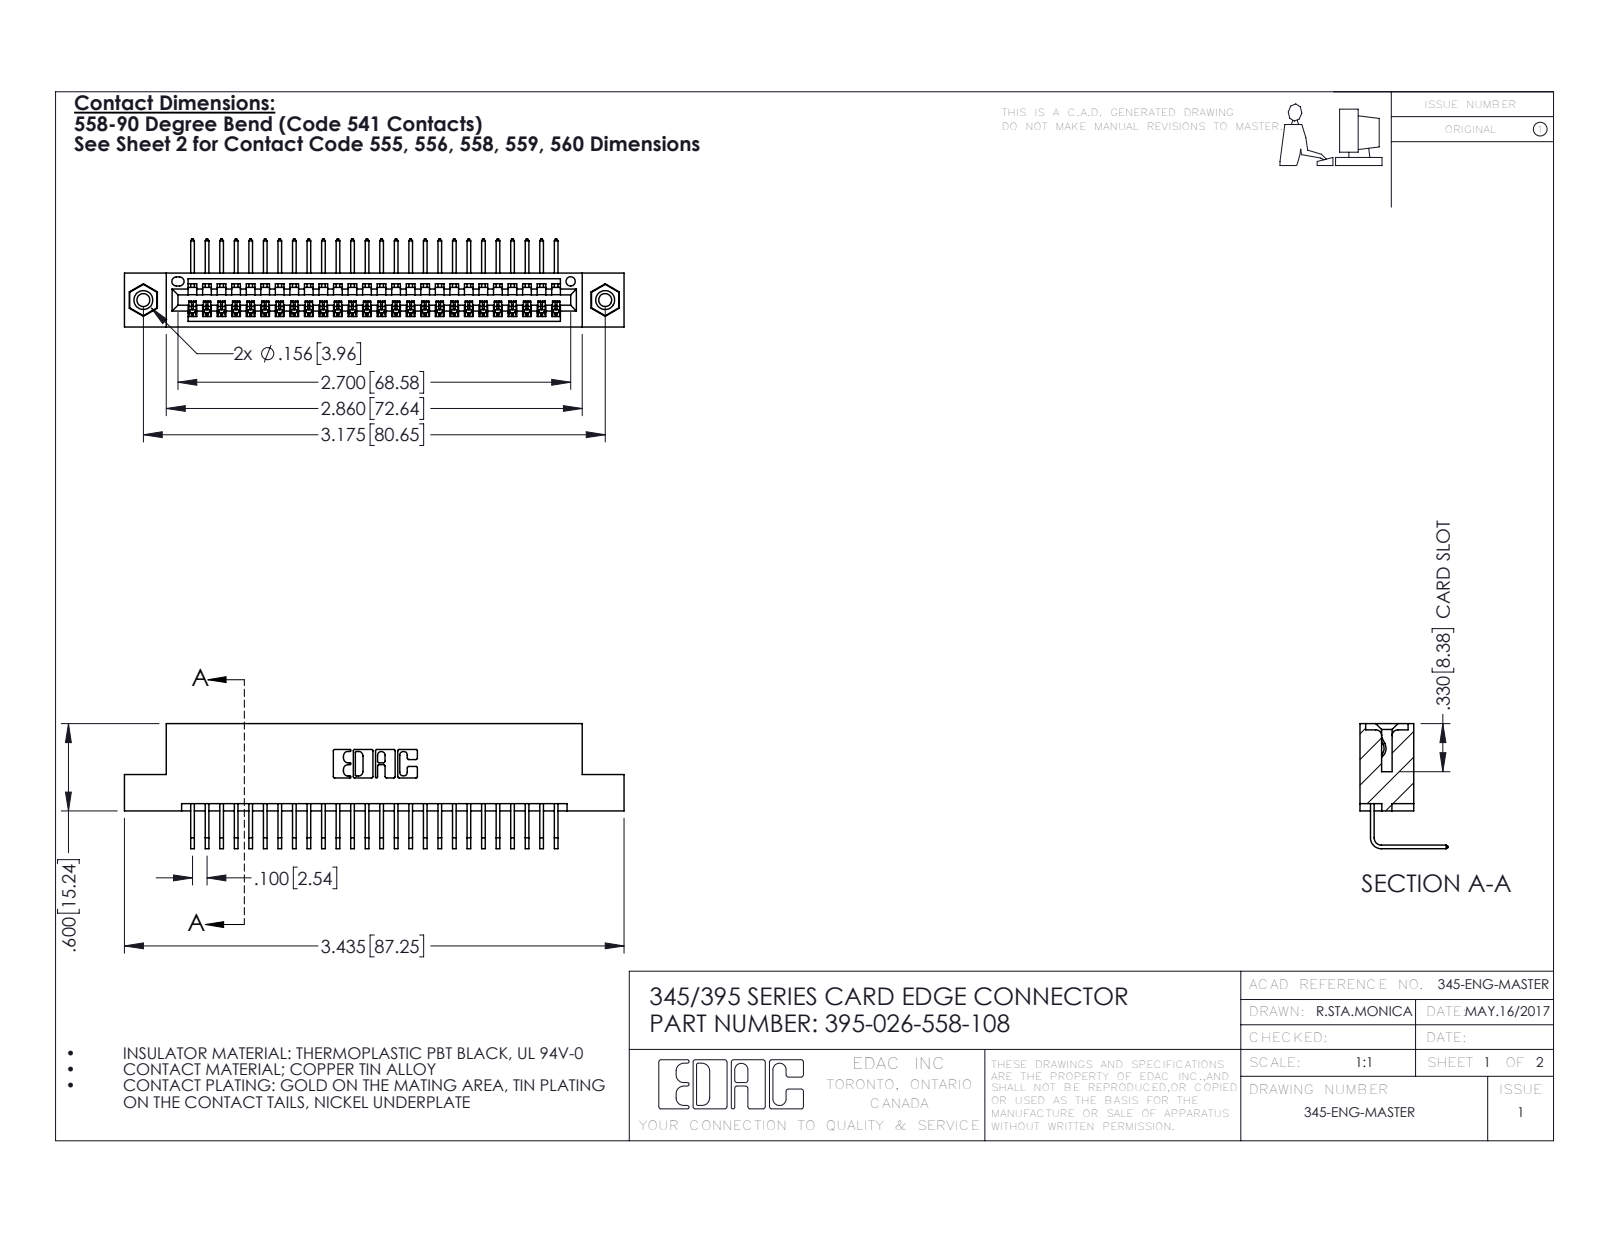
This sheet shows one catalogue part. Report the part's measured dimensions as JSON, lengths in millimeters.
{"part_name": "345-292-001_558 Tail - 2; 345-250-001_345-250-003-102; 345 Part_Flush Mounting Lugs - 0.156 Dia-TI; 395-026-558-108", "step_written_by": "SolidWorks 2016 (CONFIG_CONTROL_DESIGN)", "units": "millimeters", "bodies": {"solids": 29, "faces": 1746, "planar": 1204, "cylindrical": 526, "other": 16}, "overall_size": [87.2, 21.8, 15.4], "volume_mm3": 8240, "surface_area_mm2": 11260, "round_holes": [[2.3, 2], [3.2, 2], [4, 2], [1.6, 1]], "round_bosses_or_shafts": [[3.9, 2]], "partial_cylinders_radius": [[0.2, 52], [0.3, 22], [0.2, 6], [0.8, 6], [0.7, 3], [0.8, 2], [1, 2], [0.4, 1]], "face_to_face_distances": [1.8, 7.6, 5.1, 9.4, 2.5, 6.9, 0.6, 5.7, 3.8, 1.8], "hole_center_spacings": [6.9, 74.7, 80.6]}
